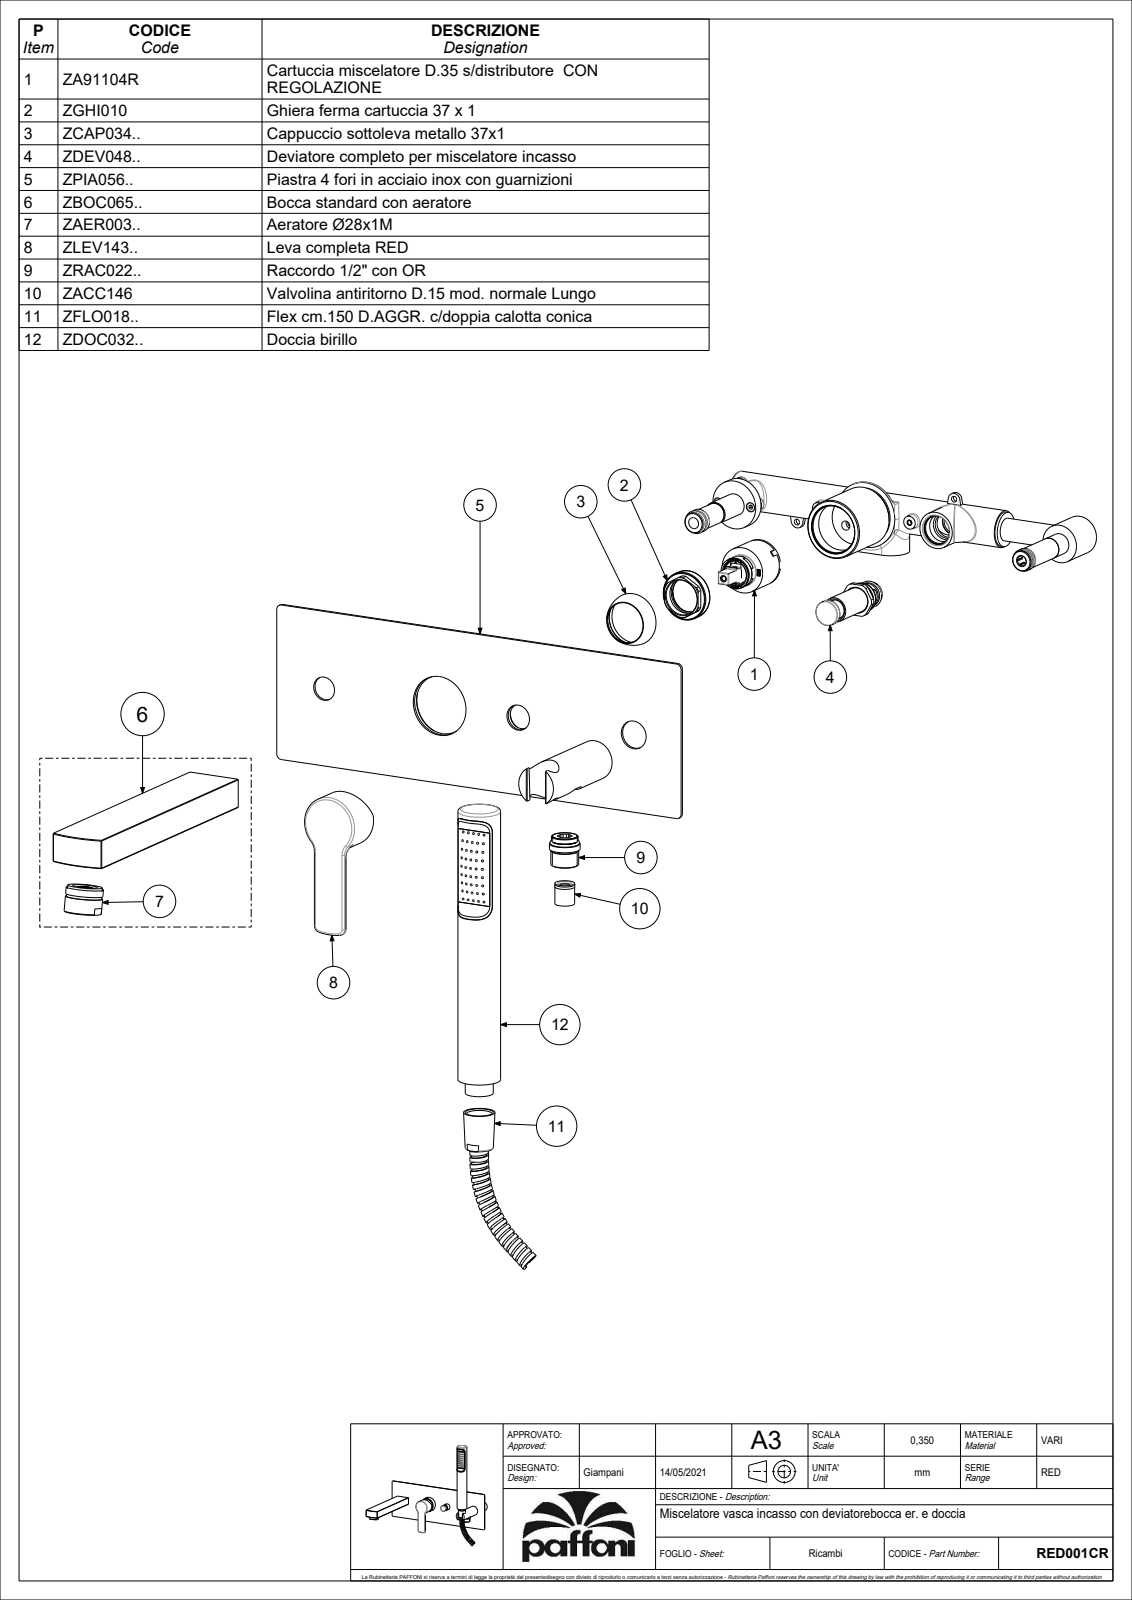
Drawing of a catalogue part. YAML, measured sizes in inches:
part_name: "RED001CR"
step_written_by: "CREO PARAMETRIC BY PTC INC, 2020044 (CONFIG_CONTROL_DESIGN)"
units: inches
bodies: {solids: 10, faces: 2935, planar: 2140, cylindrical: 452, other: 343}
overall_size: [14.051, 13.043, 8.278]
volume: 24.63
surface_area: 372.9
round_holes:
  - {diameter: 0.059, count: 45}
  - {diameter: 0.13, count: 2}
  - {diameter: 0.157, count: 2}
  - {diameter: 0.177, count: 2}
  - {diameter: 0.335, count: 2}
  - {diameter: 0.63, count: 2}
  - {diameter: 0.681, count: 2}
  - {diameter: 0.748, count: 2}
  - {diameter: 0.768, count: 2}
  - {diameter: 0.118, count: 1}
  - {diameter: 0.197, count: 1}
  - {diameter: 0.295, count: 1}
round_bosses_or_shafts:
  - {diameter: 0.866, count: 2}
  - {diameter: 1.764, count: 1}
  - {diameter: 1.693, count: 1}
  - {diameter: 1.378, count: 1}
  - {diameter: 1.26, count: 1}
  - {diameter: 1.181, count: 1}
  - {diameter: 1.102, count: 1}
  - {diameter: 1.087, count: 1}
partial_cylinders:
  - {radius: 0.02, count: 45}
  - {radius: 0.006, count: 11}
  - {radius: 0.394, count: 5}
  - {radius: 0.012, count: 4}
  - {radius: 0.059, count: 4}
  - {radius: 0.157, count: 4}
  - {radius: 0.039, count: 2}
  - {radius: 0.089, count: 2}
face_to_face_distances: [0.079, 0.866, 1.654, 1.933, 1.854, 0.177, 2.11, 2.031, 3.248, 3.327]
hole_center_spacings: [0.311, 0.542, 0.256, 0.788, 0.512, 1.039, 0.177, 0.768]
